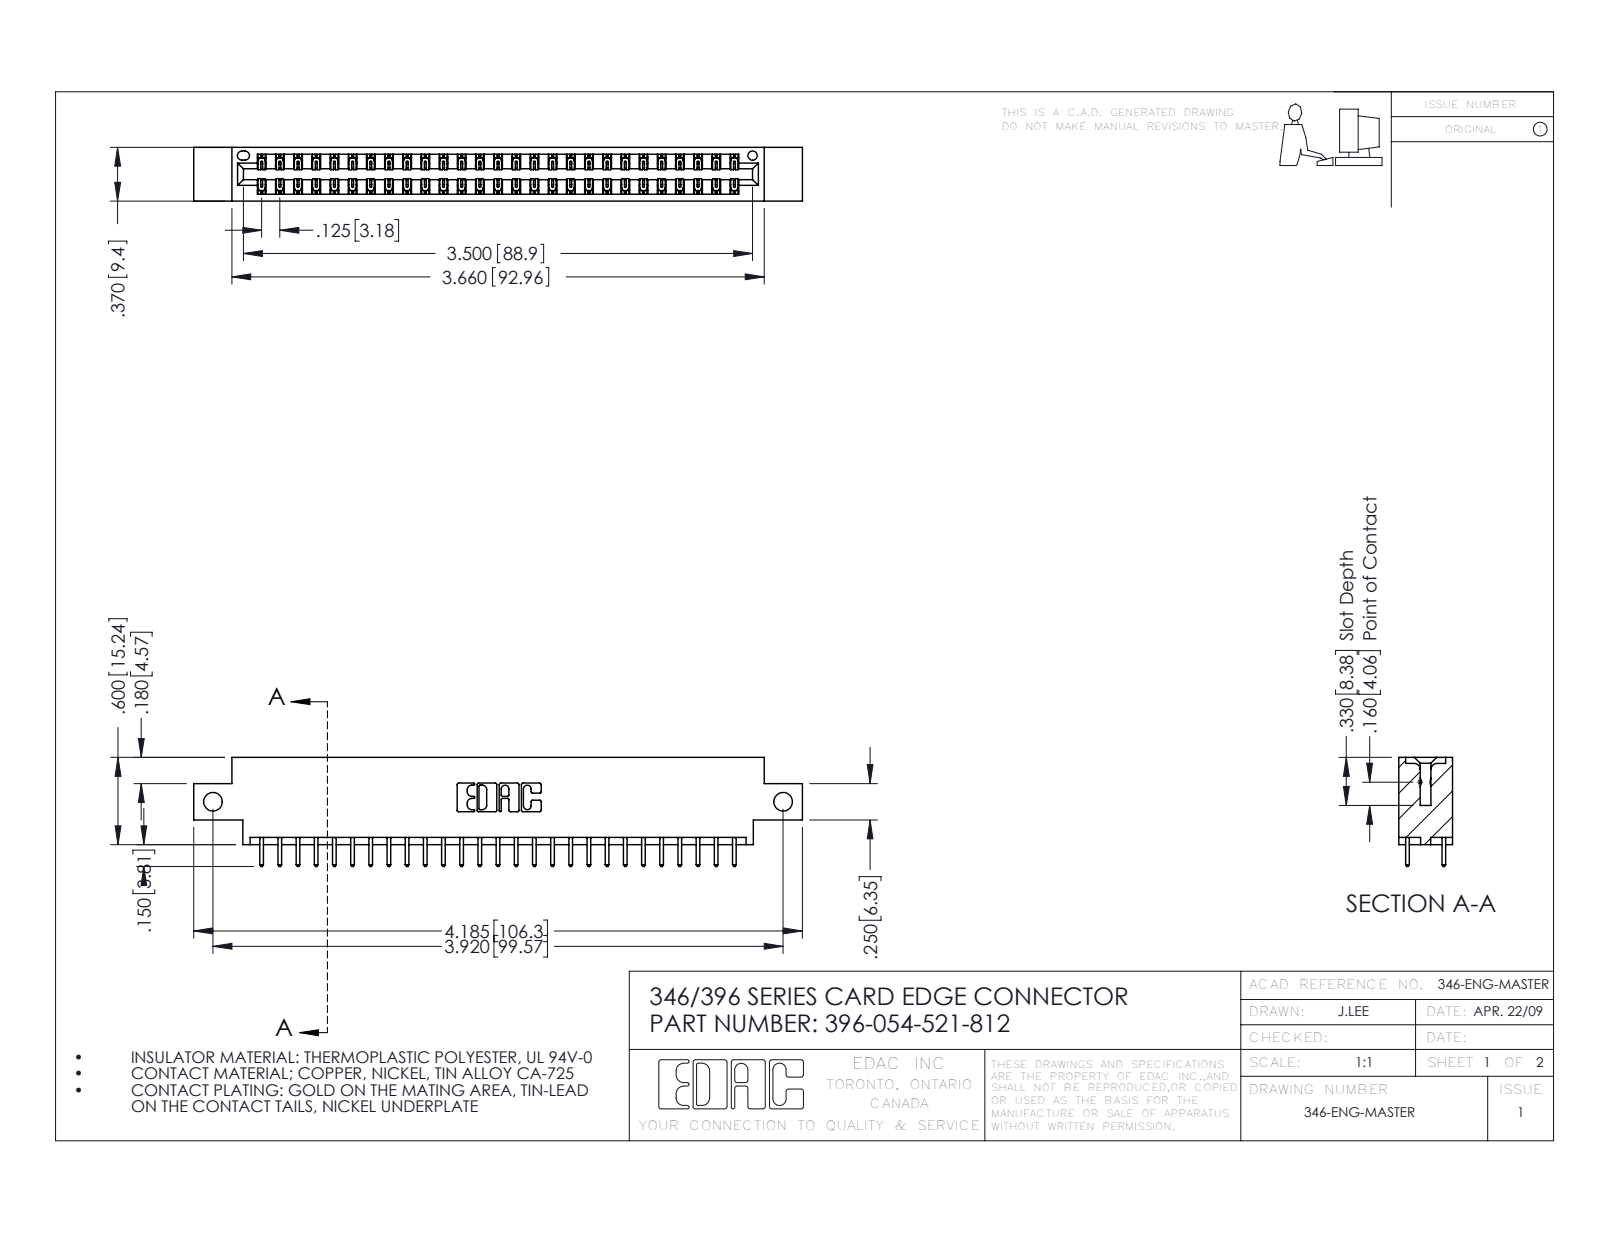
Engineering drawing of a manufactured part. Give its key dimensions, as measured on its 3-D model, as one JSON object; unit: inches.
{"part_name": "396-054-521-812; 346 Part_0.170 Offset - Side Mount; 345-292-001_345-293-121", "step_written_by": "SolidWorks 2016 (CONFIG_CONTROL_DESIGN)", "units": "inches", "bodies": {"solids": 55, "faces": 2934, "planar": 1970, "cylindrical": 964, "other": 0}, "overall_size": [4.185, 0.75, 0.37], "volume_in3": 0.609, "surface_area_in2": 20.74, "round_holes": [[0.128, 2], [0.064, 1]], "partial_cylinders_radius": [[0.006, 81], [0.01, 54], [0.01, 22], [0.007, 6], [0.031, 6], [0.026, 3], [0.014, 2], [0.022, 2]], "face_to_face_distances": [0.048, 0.322, 0.37, 0.25, 0.072, 0.298, 0.025, 0.275, 0.148, 0.222], "hole_center_spacings": [3.92]}
